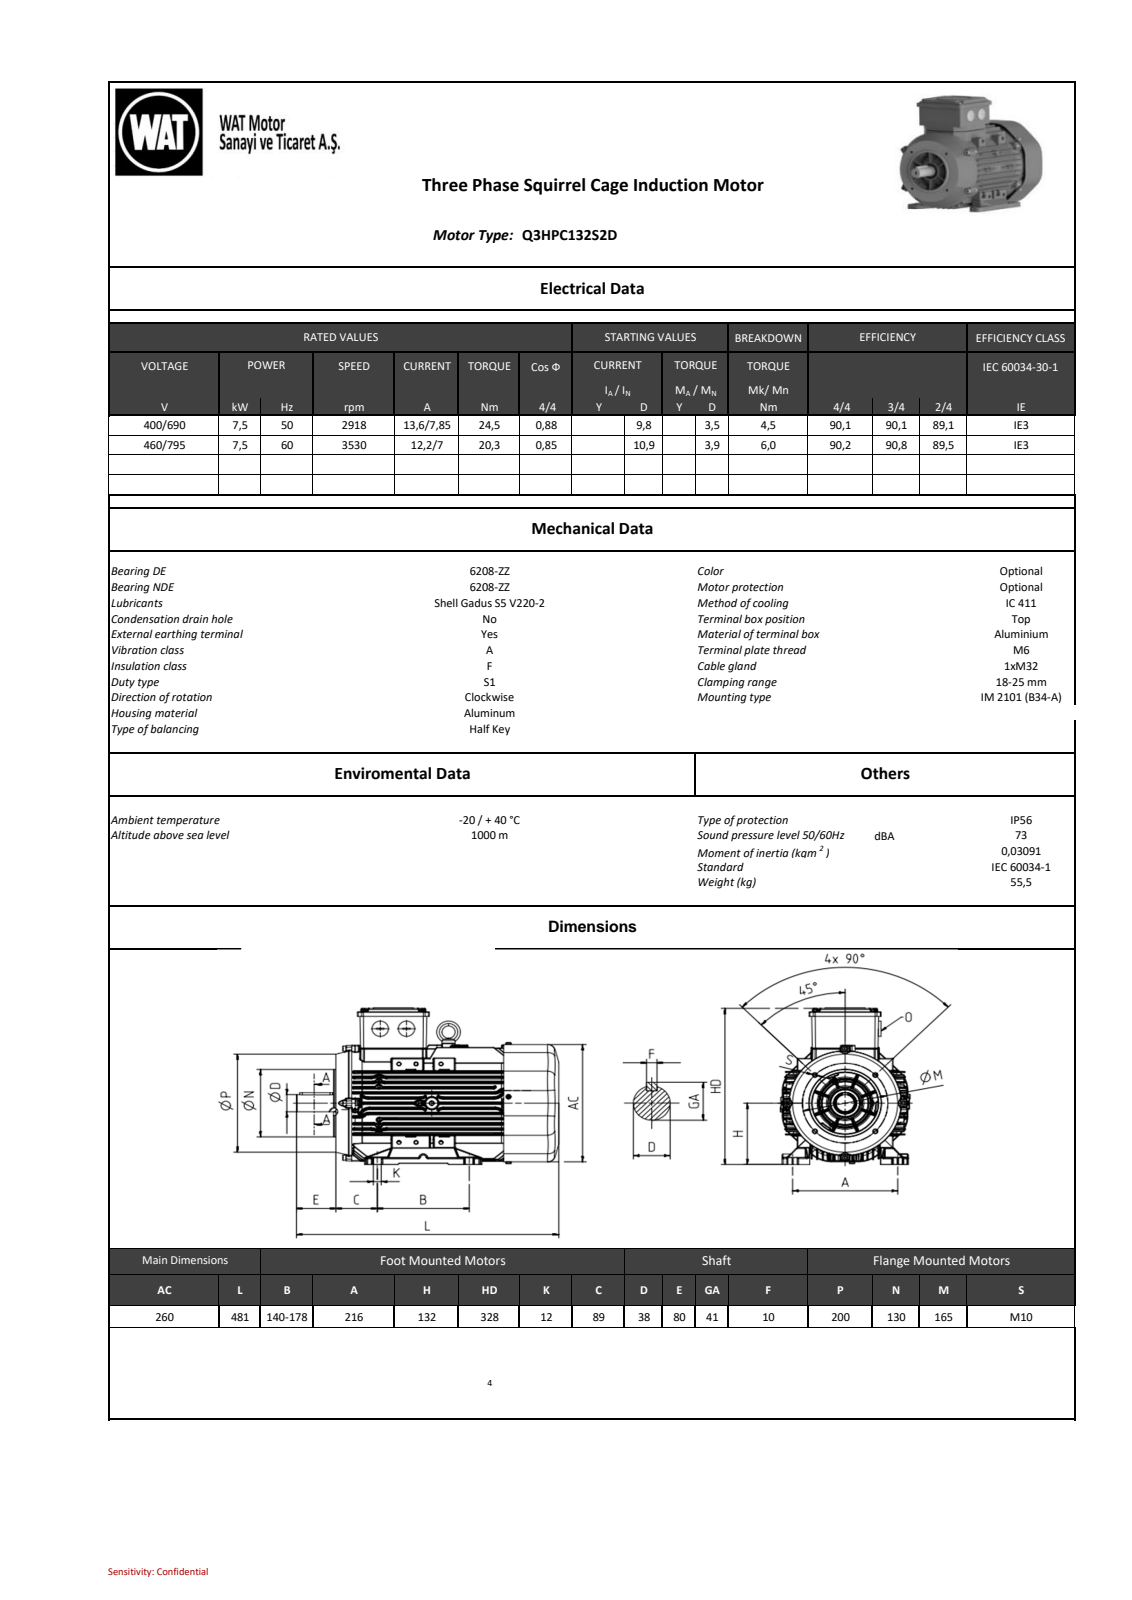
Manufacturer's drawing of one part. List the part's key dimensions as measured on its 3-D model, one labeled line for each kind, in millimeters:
Part name (STEP PRODUCT): QH series_132_B34a_stp_objects
STEP written by: SIEMENS PLM Software NX2206.8101 (AP203_CONFIGURATION_CONTROLLED_3D_DESIGN_OF_MECHANICAL_PARTS_AND_ASSEMBLIES_MIM_LF)
Units: millimetres
Bodies: 0 solids, 7863 faces (1886 planar, 3367 cylindrical, 2610 other)
Overall size (bounding box): 480.49 × 323.2 × 260.12
Round holes (diameter × count): ⌀8.48 ×2, ⌀5.5 ×1, ⌀8.48 ×1, ⌀12 ×1, ⌀14 ×1, ⌀24.4 ×1, ⌀82 ×1, ⌀180 ×1
Round bosses / shafts (diameter × count): ⌀8 ×8, ⌀13.4 ×4, ⌀13 ×4, ⌀38 ×3, ⌀230.5 ×1, ⌀130 ×1, ⌀86.77 ×1, ⌀45 ×1
Partial cylindrical surfaces — rounded edges, fillets, slot ends (radius × count): R1 ×914, R0.8 ×889, R0.5 ×74, R3 ×72, R2 ×54, R5 ×20, R60 ×16, R1.15 ×15
Main face-to-face distances: 10.42, 10.56, 1.5, 10.28, 20.84, 125.58, 94.46, 104.9, 115.18, 94.48
Hole centre spacings: 74.95, 143, 178.91, 217.51
